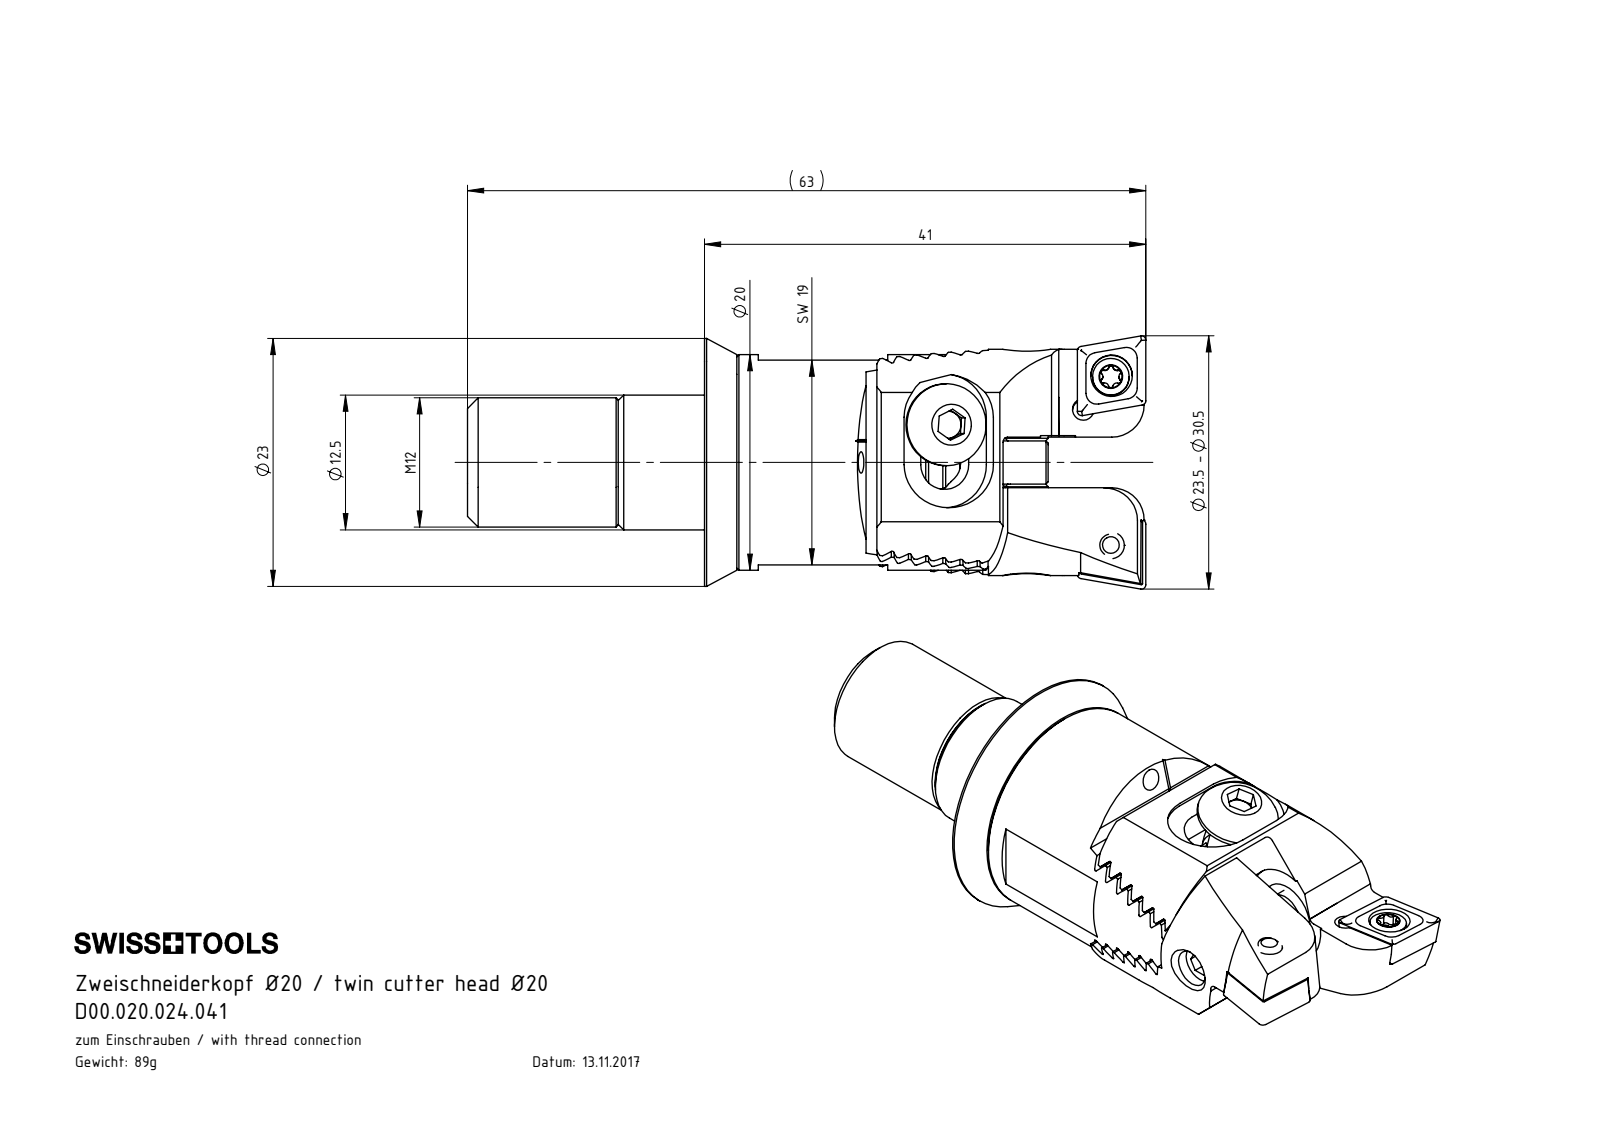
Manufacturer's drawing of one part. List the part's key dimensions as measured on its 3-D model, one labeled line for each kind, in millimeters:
Part name (STEP PRODUCT): Z20-ER1.002.008_A_PreviewCfg; Z20-WCA.001.015; Z20-ER3.001.007_A; CCMT060204 (+7 more)
STEP written by: SolidWorks 2017 (CONFIG_CONTROL_DESIGN)
Units: millimetres
Bodies: 14 solids, 764 faces (340 planar, 227 cylindrical, 197 other)
Overall size (bounding box): 62.96 × 23.5 × 23
Volume: 11 454 mm³ · Surface area: 9 433 mm²
Round holes (diameter × count): ⌀2 ×6, ⌀3.3 ×3, ⌀1 ×2, ⌀2.05 ×2, ⌀2.8 ×2, ⌀3.85 ×2, ⌀5 ×2, ⌀2.5 ×1, ⌀3.5 ×1, ⌀6.8 ×1, ⌀8.5 ×1, ⌀9.1 ×1
Round bosses / shafts (diameter × count): ⌀4 ×4, ⌀7.6 ×2, ⌀3.4 ×2, ⌀2.5 ×2, ⌀23 ×1, ⌀20 ×1, ⌀12 ×1, ⌀8 ×1
Partial cylindrical surfaces — rounded edges, fillets, slot ends (radius × count): R0.12 ×26, R0.21 ×12, R0.36 ×10, R1 ×8, R0.5 ×4, R2.3 ×4, R4 ×4, R0.36 ×2
Main face-to-face distances: 1.43, 2.86, 3, 5.71, 4.29, 4.28, 7.14, 2.85, 2.57, 7.15
Hole centre spacings: 3.99, 4.09, 6, 13.08, 13.17, 15.96, 9.77, 11.6
